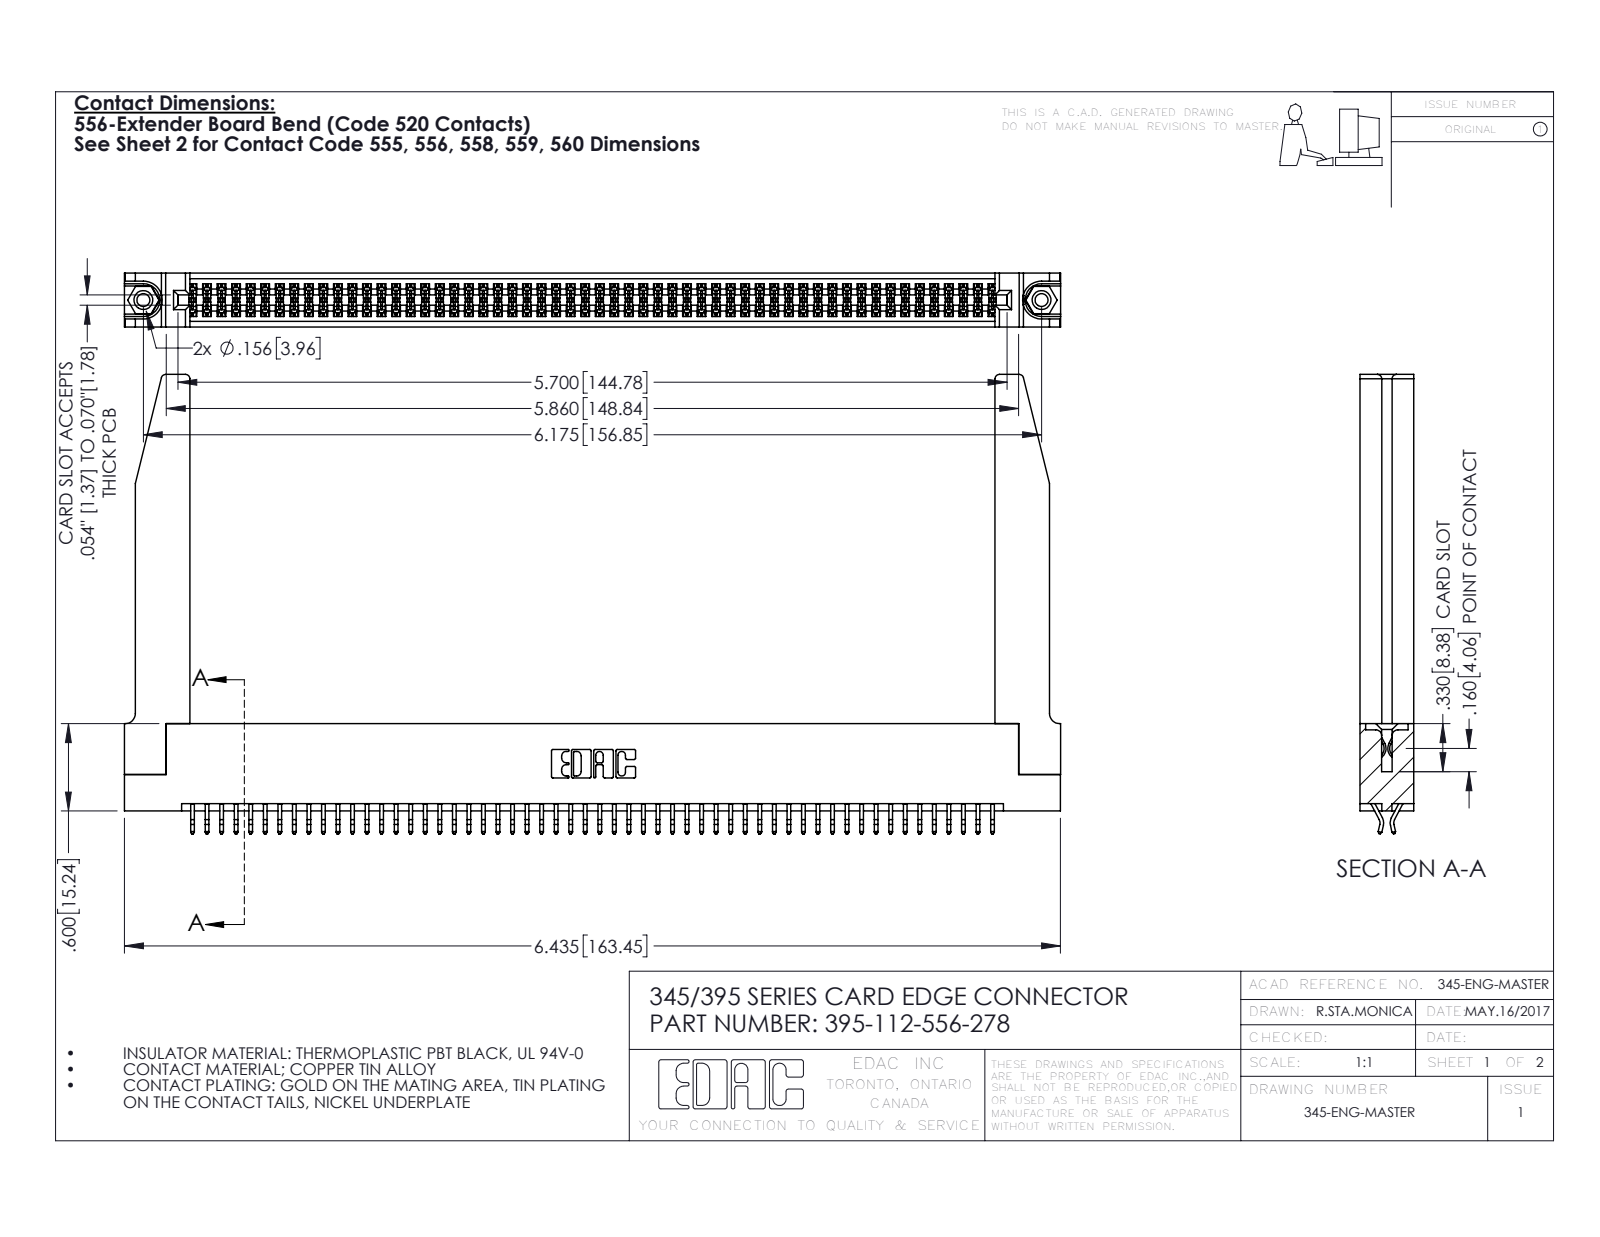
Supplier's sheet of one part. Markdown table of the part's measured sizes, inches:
| quantity | value |
| --- | --- |
| part name | 395-112-556-278; 345-250-001_345-250-001-102; 345-220-078_345-220-078; 345-292-001_556 Tail (+1 more) |
| STEP written by | SolidWorks 2016 (CONFIG_CONTROL_DESIGN) |
| units | inches |
| bodies | 117 solids, 6632 faces (4366 planar, 2214 cylindrical, 52 other) |
| overall size | 6.436 × 3.157 × 0.37 |
| volume | 1.451 in³ |
| surface area | 47.54 in² |
| round holes (diameter × count) | 0.089 × 2, 0.125 × 2, 0.156 × 2, 0.064 × 1 |
| round bosses / shafts (diameter × count) | 0.155 × 2 |
| partial cylindrical surfaces (radius × count) | 0.006 × 168, 0.01 × 22, 0.03 × 8, 0.007 × 6, 0.031 × 6, 0.026 × 3, 0.01 × 2, 0.014 × 2 |
| main face-to-face distances | 0.072, 0.37, 0.298, 0.2, 0.025, 0.098, 0.272, 0.225, 0.175, 0.148 |
| hole center spacings | 0.27, 5.939, 6.175 |
